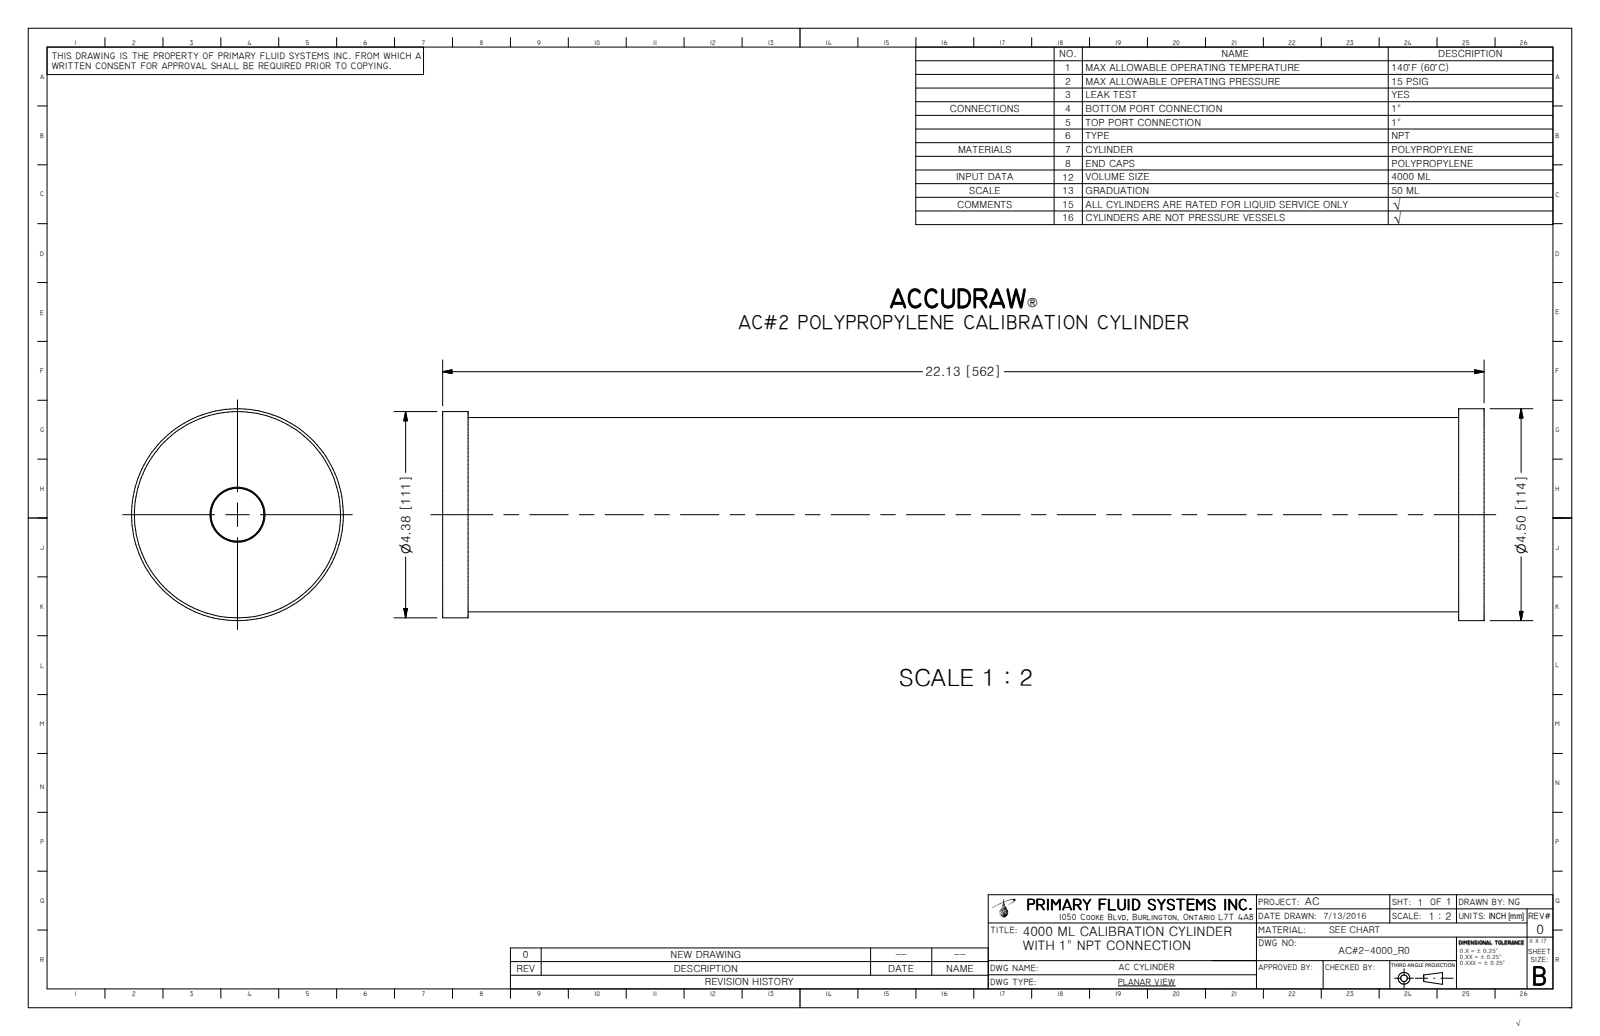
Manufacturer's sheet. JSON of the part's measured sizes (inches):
{"part_name": "AC#2-4000_R0; AC-2B-2000; AC-4000-TUBE; AC-2T-4000", "step_written_by": "Autodesk Inventor 2009 (AUTOMOTIVE_DESIGN)", "units": "inches", "bodies": {"solids": 3, "faces": 20, "planar": 8, "cylindrical": 6, "other": 6}, "overall_size": [22.13, 4.5, 4.5], "volume_in3": 32.21, "surface_area_in2": 608.2, "round_holes": [[4.005, 1]], "round_bosses_or_shafts": [[4.5, 1], [4.125, 1], [4.09, 1], [3.38, 1], [2.95, 1]], "face_to_face_distances": [0.75, 21.38, 22.13, 20.63, 21.59, 20.84, 0.21, 0.54, 0.54, 0.21]}
